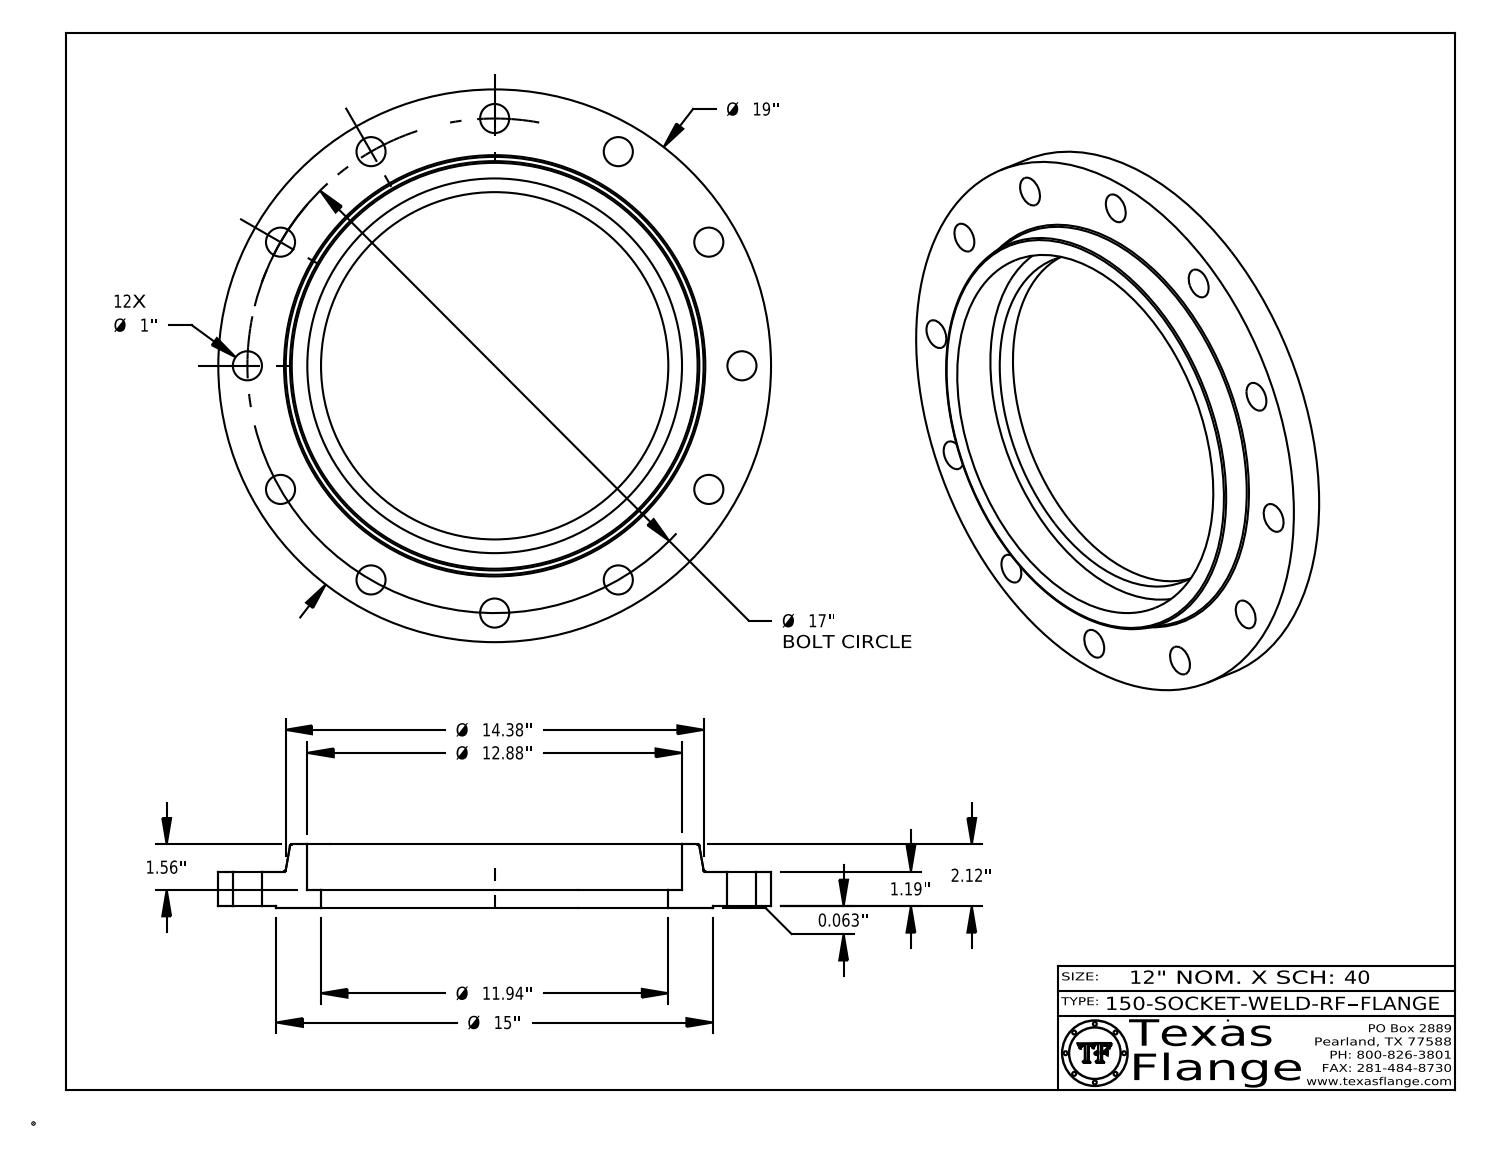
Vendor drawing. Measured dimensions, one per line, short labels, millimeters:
name: 150-SOCKET-WELD-RF
written by: CATIA V5 STEP AP214 (AUTOMOTIVE_DESIGN)
unit: mm
bodies: 1 solid, 428 faces (370 planar, 52 cylindrical, 6 other)
size: 482.6 × 482.6 × 55.4
volume: 3 472 000 mm³; area: 363 300 mm²
holes: 12× ⌀25.4, 1× ⌀12.6, 1× ⌀303.2, 1× ⌀327.2
bosses: 8× ⌀0.8, 1× ⌀482.6, 1× ⌀381, 1× ⌀9.9
face distances: 30.2, 1.6, 31.8, 55.4, 53.8, 23.6, 15.8, 14.2, 16, 39.6
hole spacings: 215.9, 417.1, 111.8, 305.3, 373.9, 111.8, 305.3, 373.9
